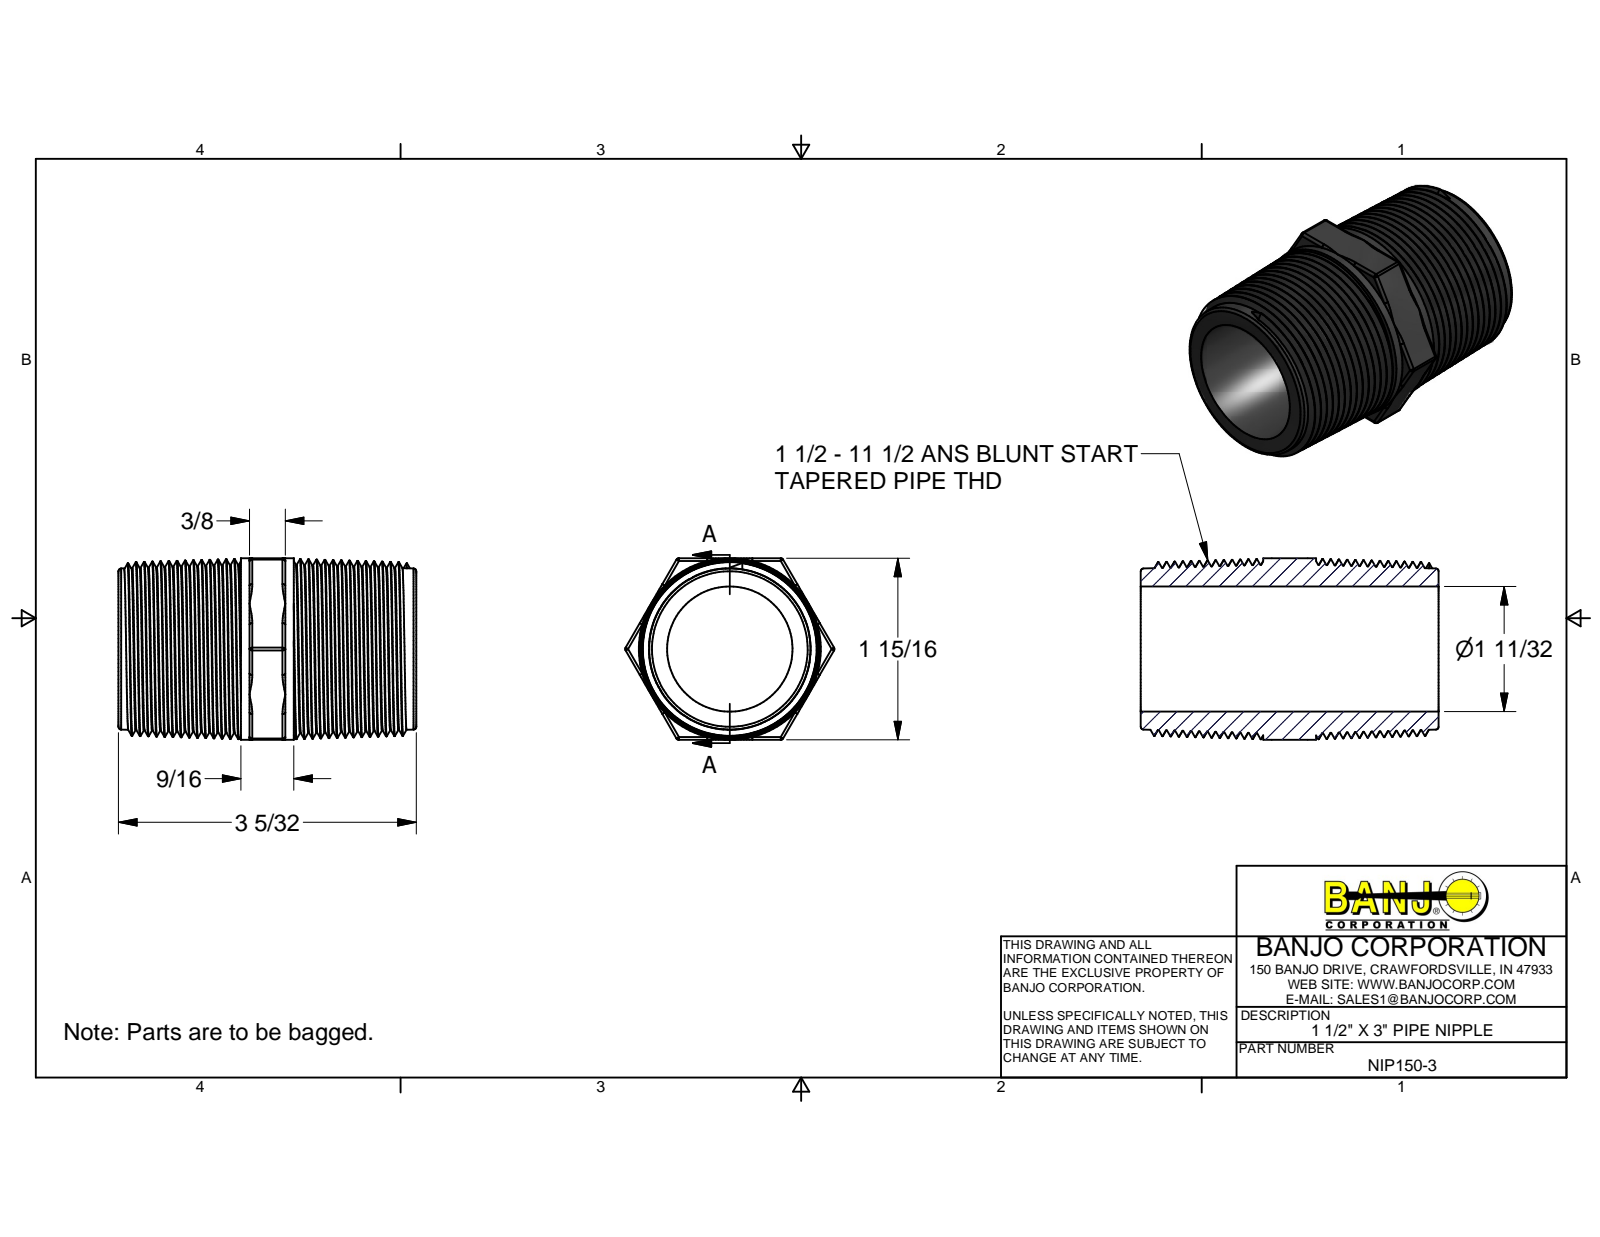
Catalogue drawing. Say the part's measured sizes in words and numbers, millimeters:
The part is named "NIP150-3". Its 3-D file was written by "Autodesk Inventor 2013 (AUTOMOTIVE_DESIGN)". It is 1 solid with 135 faces: 24 planar, 33 cylindrical and 78 other. Overall it measures 80.3 by 56.4 by 49 millimeters. Its volume is 66 060 cubic millimeters and its surface area 29 450 square millimeters. Round holes: 1 of diameter 33.8. Round bosses or shafts: 1 of diameter 49. Partial cylindrical surfaces (rounded edges, fillets, slot ends): 18 of radius 0.8. The main face-to-face distances are 49, 80.3, 33, 47.2, 35.3, 45, 2.3, 11.9, 14.2, 9.7.
